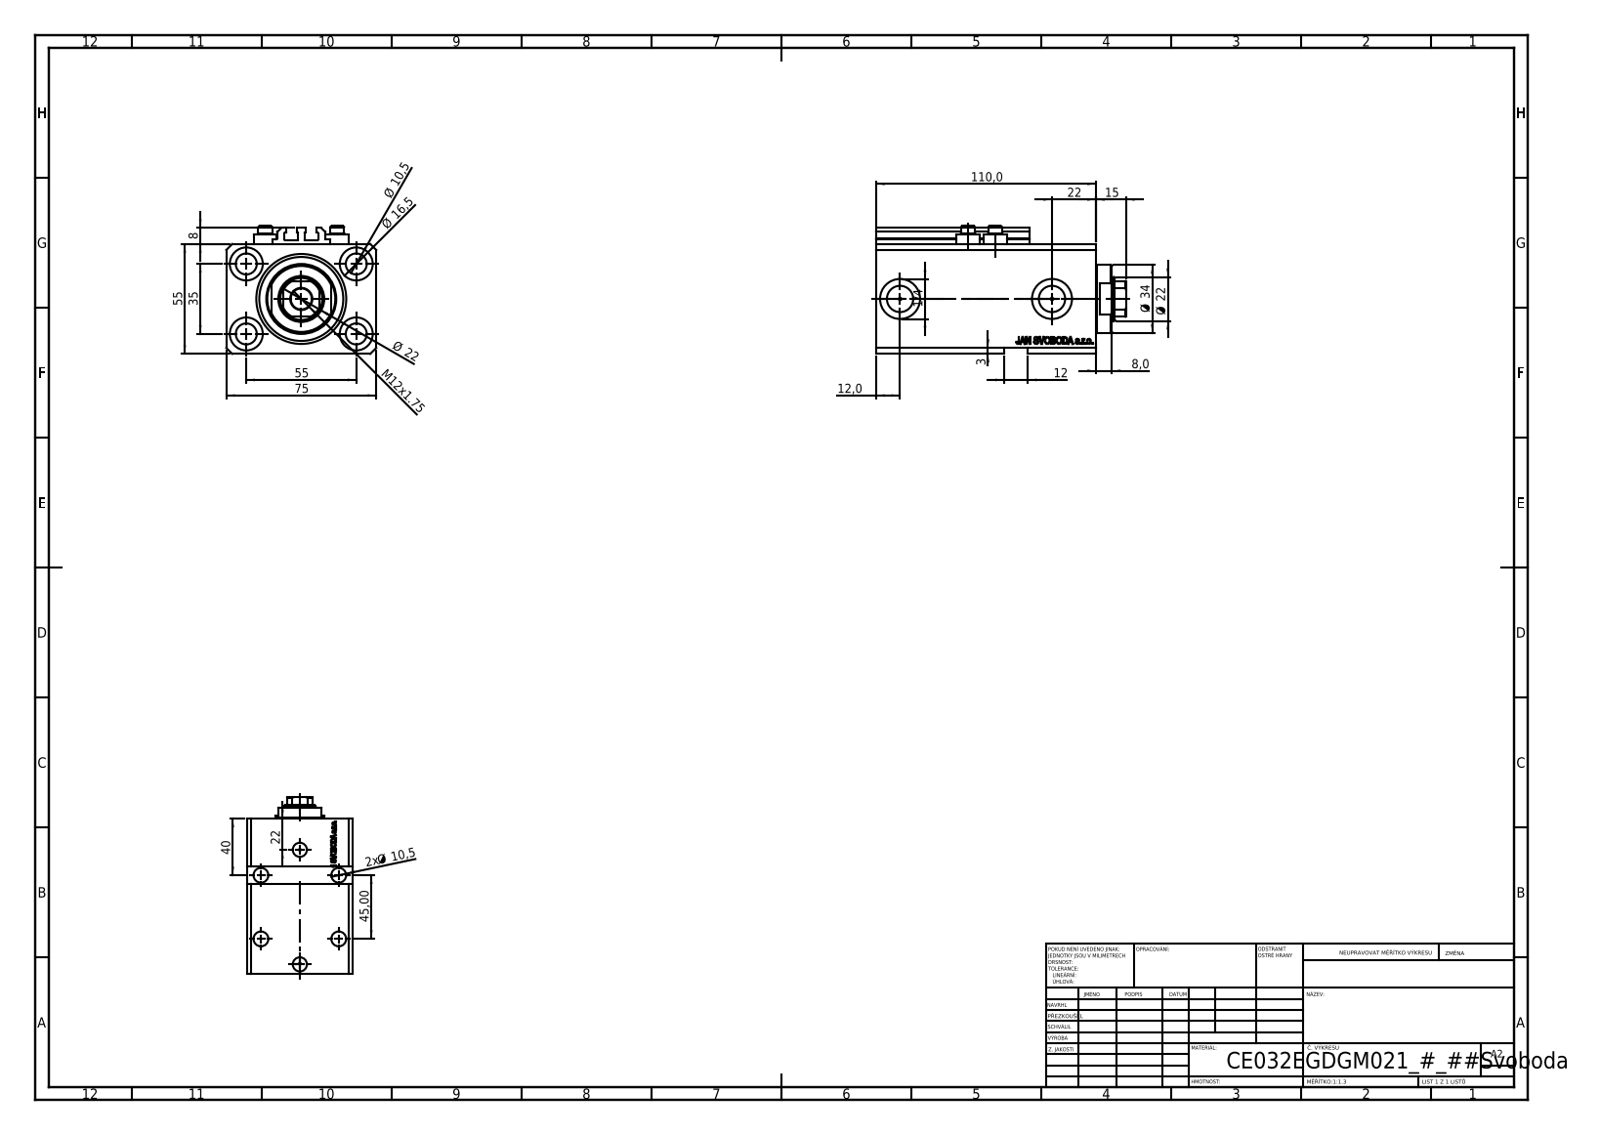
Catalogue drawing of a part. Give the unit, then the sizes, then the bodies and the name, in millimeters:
Units: millimetres
Overall size (bounding box): 125 × 75 × 64
Round holes (diameter × count): ⌀10.5 ×9, ⌀1.25 ×4, ⌀4 ×4, ⌀16.5 ×4, ⌀10 ×2, ⌀13.16 ×2, ⌀20 ×2, ⌀22 ×1, ⌀32 ×1, ⌀45 ×1
Round bosses / shafts (diameter × count): ⌀11.6 ×4, ⌀7 ×4, ⌀34 ×1
Partial cylindrical surfaces — rounded edges, fillets, slot ends (radius × count): R0.2 ×10, R10.5 ×1
Main face-to-face distances: 55, 75, 15, 110, 95, 9.9, 3, 85.1, 100.1, 57
Hole centre spacings: 32.6, 32.87, 55, 68.74, 13.6, 14.09, 23.05, 25.81
Volume: 377 718 mm³ · Surface area: 96 791 mm²
Bodies: 8 solids, 1100 faces (518 planar, 158 cylindrical, 424 other)
Part name (STEP PRODUCT): V250CE_E_Body; V250CE_VC_E; ALLEN BOLT V250CE; V250CE_C_VCP
STEP written by: SolidWorks 2019 (CONFIG_CONTROL_DESIGN)
